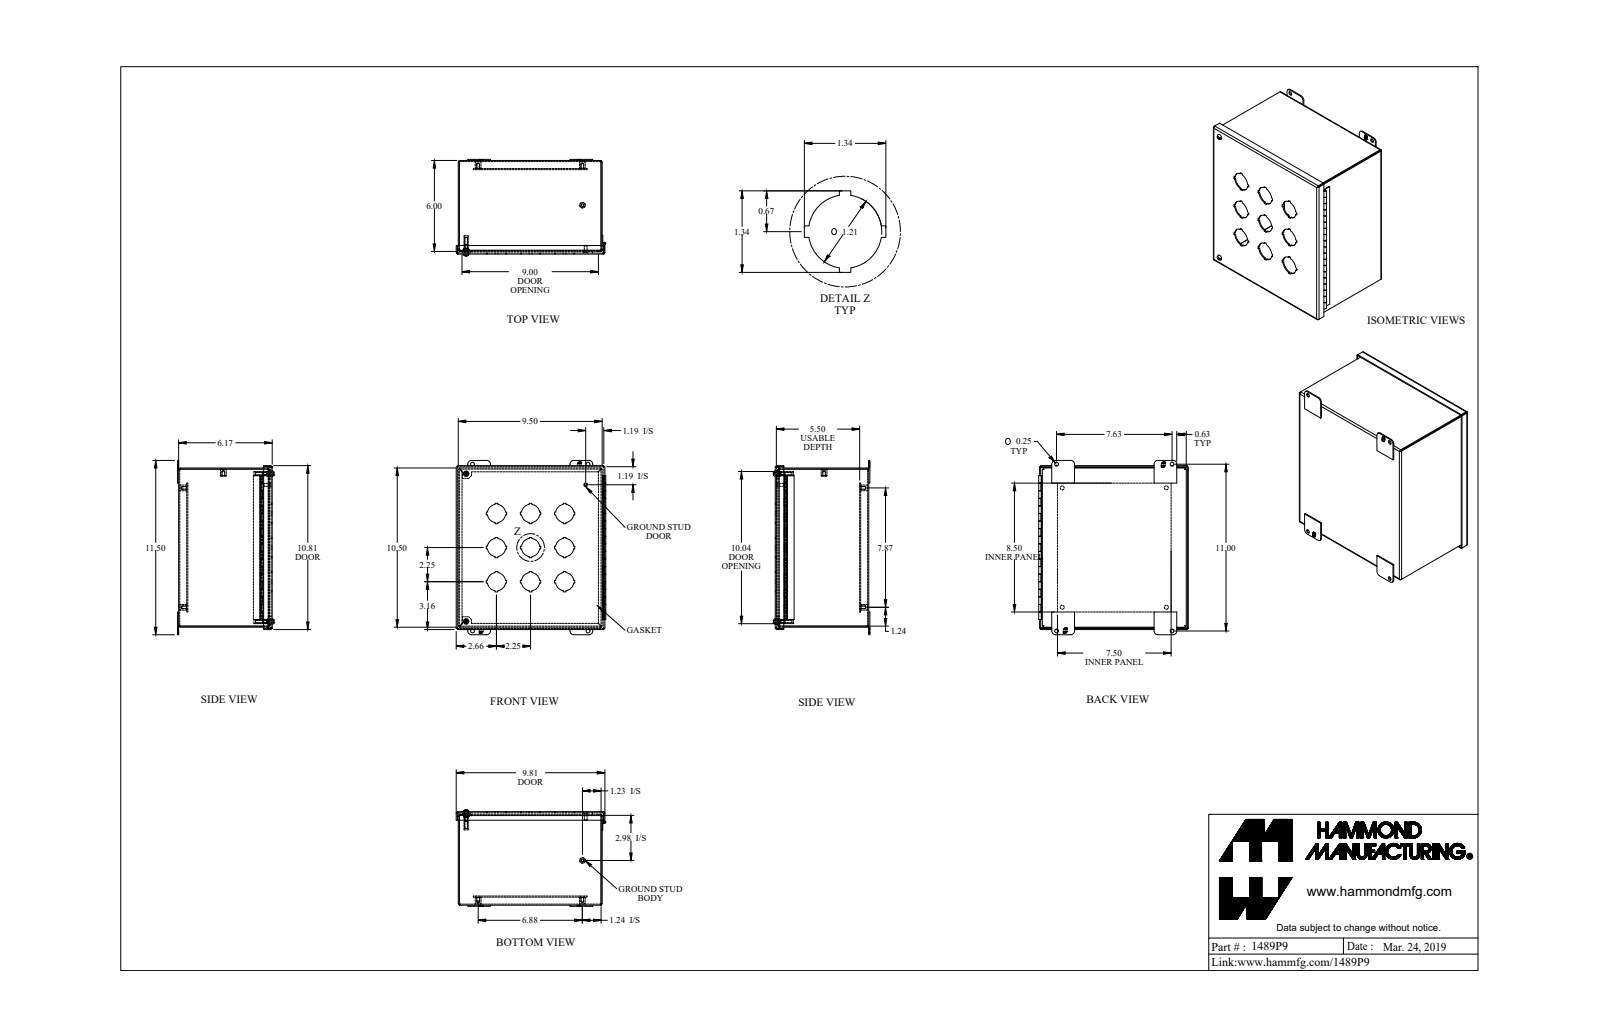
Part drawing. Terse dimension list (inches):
name: 1489P9_Default
written by: SolidWorks 2019 (CONFIG_CONTROL_DESIGN)
unit: in
bodies: 21 solids, 836 faces (572 planar, 206 cylindrical, 58 other)
size: 11.5 × 9.873 × 6.371
volume: 43.92 in³; area: 1 174 in²
holes: 9× ⌀1.21, 6× ⌀0.25, 5× ⌀0.156, 4× ⌀0.265, 2× ⌀0.159, 2× ⌀0.406
bosses: 5× ⌀0.375, 2× ⌀0.39, 2× ⌀0.275, 2× ⌀0.19, 2× ⌀0.148, 1× ⌀0.25, 1× ⌀0.188, 1× ⌀0.174
rounds: 12× R0.036, 12× R0.108, 8× R0.25, 2× R0.16, 2× R0.171, 1× R0.125
face distances: 0.072, 6.1, 5.568, 0.532, 9.428, 10.428, 6.172, 6.028, 0.604, 5.64
hole spacings: 2.25, 3.182, 5.031, 6.875, 4.5, 7.417, 9.75, 1.607
